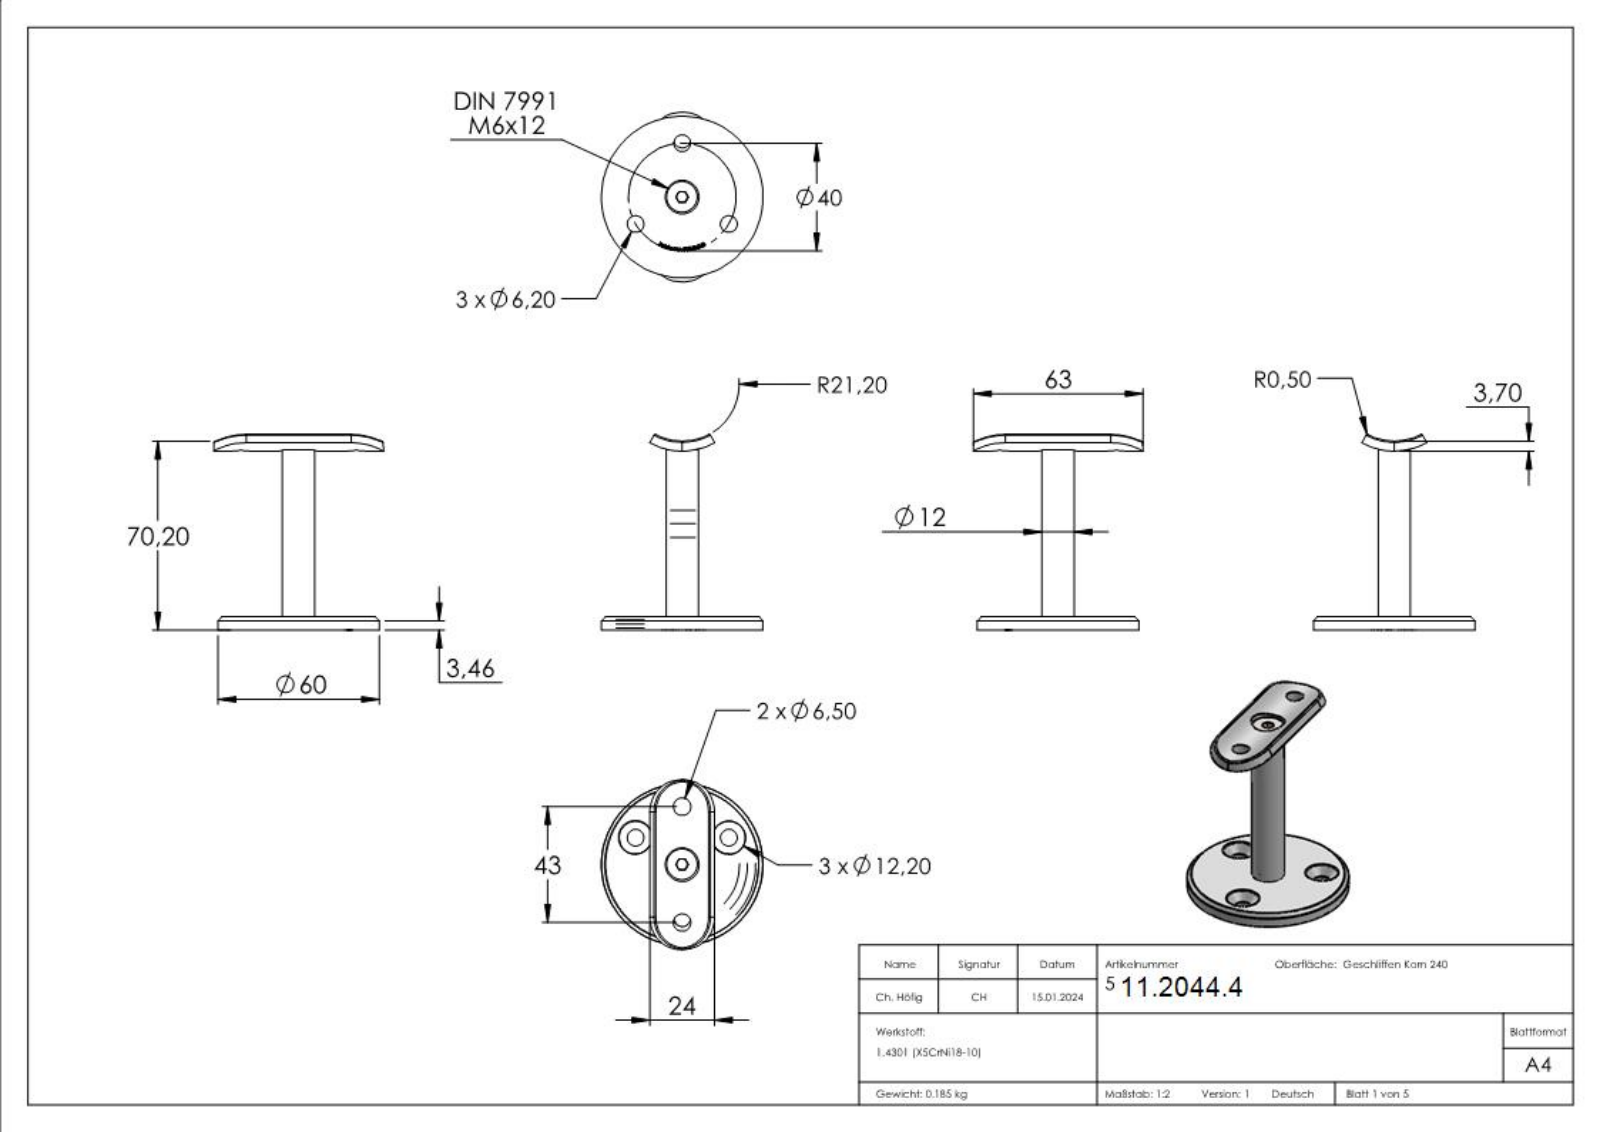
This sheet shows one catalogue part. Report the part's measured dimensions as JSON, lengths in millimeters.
{"part_name": "50343-240 Teil3_50343-240 Teil3; 5034X-240 Teil1_50343-240 Teil1; 5034X-240 Teil2_5034X-240 Teil2; socket countersunk head screw_din_DIN 7991 - M6 x 12 --- 12S (+1 more)", "step_written_by": "SolidWorks 2018 (CONFIG_CONTROL_DESIGN)", "units": "millimeters", "bodies": {"solids": 5, "faces": 372, "planar": 161, "cylindrical": 43, "other": 168}, "overall_size": [72.65, 63, 60], "volume_mm3": 24157, "surface_area_mm2": 13806, "round_holes": [[6.2, 3], [6.5, 3], [12.2, 3], [5, 1], [12.5, 1]], "round_bosses_or_shafts": [[60, 1], [12, 1], [11.57, 1], [6, 1]], "partial_cylinders_radius": [[12, 4], [0.5, 2], [7.1, 1], [21.2, 1], [24.9, 1]], "face_to_face_distances": [5, 67, 62, 0.45, 69.2, 4.55, 66.55, 68.75, 64.2, 2.2], "hole_center_spacings": [20, 34.64, 20.79, 21.5, 35.95, 1.5, 41.5, 43]}
